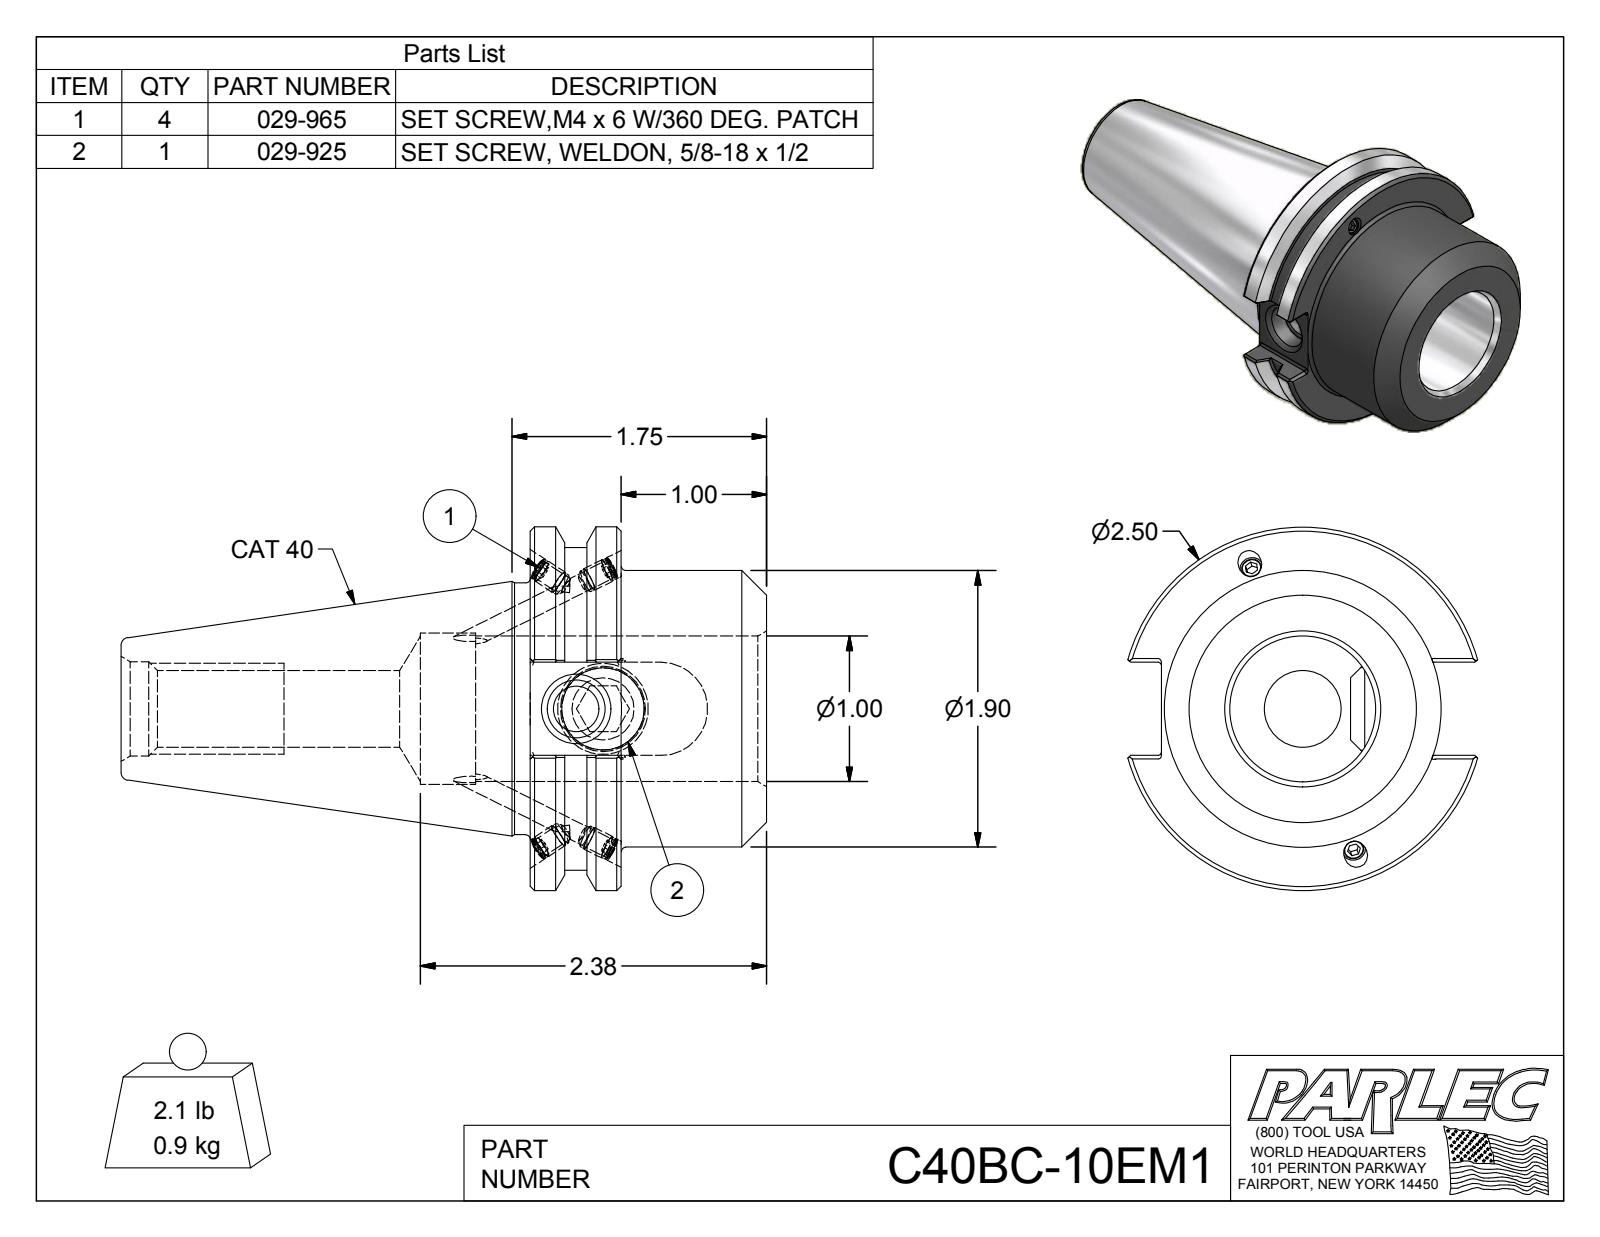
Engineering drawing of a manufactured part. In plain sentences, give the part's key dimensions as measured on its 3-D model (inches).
The part is named "C40BC-10EM1; C40BC-10EM1-1; 029-965; 029-925". Its 3-D file was written by "Autodesk Inventor 2012 (AUTOMOTIVE_DESIGN)". It is 6 solids with 187 faces: 91 planar, 54 cylindrical and 42 other. Overall it measures 4.437 by 2.5 by 2.406 inches. Its volume is 7.211 cubic inches and its surface area 45.65 square inches. Round holes: 4 of diameter 0.13, 4 of diameter 0.161, 1 of diameter 0.315, 1 of diameter 0.399, 1 of diameter 0.527, 1 of diameter 0.565, 1 of diameter 0.625, 1 of diameter 0.648, 1 of diameter 1, 1 of diameter 1.04. Round bosses or shafts: 4 of diameter 0.165, 4 of diameter 0.157, 1 of diameter 2.5, 1 of diameter 2.219, 1 of diameter 1.9, 1 of diameter 1.73. Partial cylindrical surfaces (rounded edges, fillets, slot ends): 10 of radius 0.02, 1 of radius 0.32. The main face-to-face distances are 0.625, 1, 1.625, 0.64, 1.86, 2.812, 3.437, 4.437, 0.061, 1.8. The hole center spacings are 0.185.
